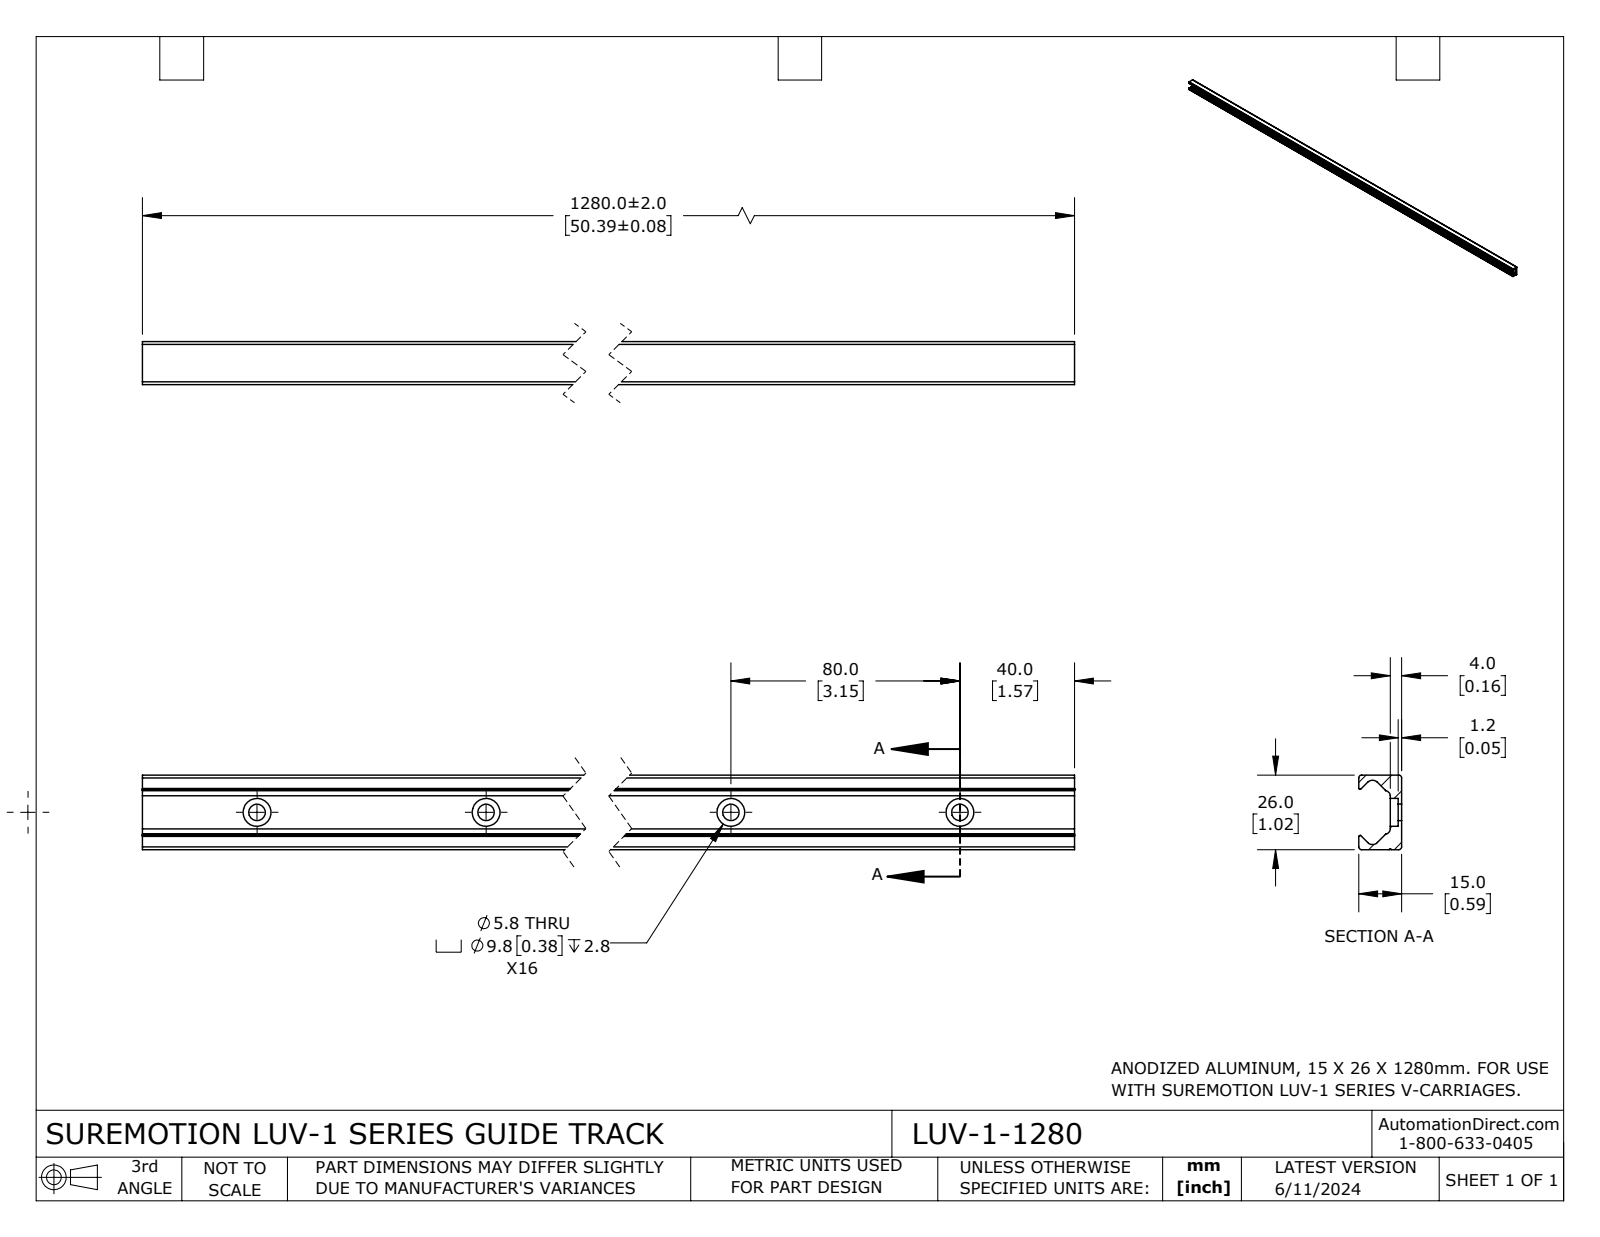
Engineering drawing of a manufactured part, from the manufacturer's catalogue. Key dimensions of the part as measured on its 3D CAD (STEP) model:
Part name (STEP PRODUCT): LUV-1-1280
STEP written by: SolidWorks 2023 (CONFIG_CONTROL_DESIGN)
Units: millimetres
Bodies: 1 solid, 108 faces (29 planar, 79 cylindrical, 0 other)
Overall size (bounding box): 1280 × 26.01 × 15.01
Volume: 230 477 mm³ · Surface area: 135 771 mm²
Round holes (diameter × count): ⌀5.79 ×16, ⌀9.75 ×16
Partial cylindrical surfaces — rounded edges, fillets, slot ends (radius × count): R0.99 ×4, R0.51 ×2, R0.64 ×2, R0.76 ×2, R1.78 ×2, R2.39 ×2, R0.33 ×1
Main face-to-face distances: 26.02, 4.01, 15.02, 11.01, 17.27, 1.21, 2.8, 13.81, 1280
Hole centre spacings: 80, 160, 240, 320, 400, 480, 560, 640
